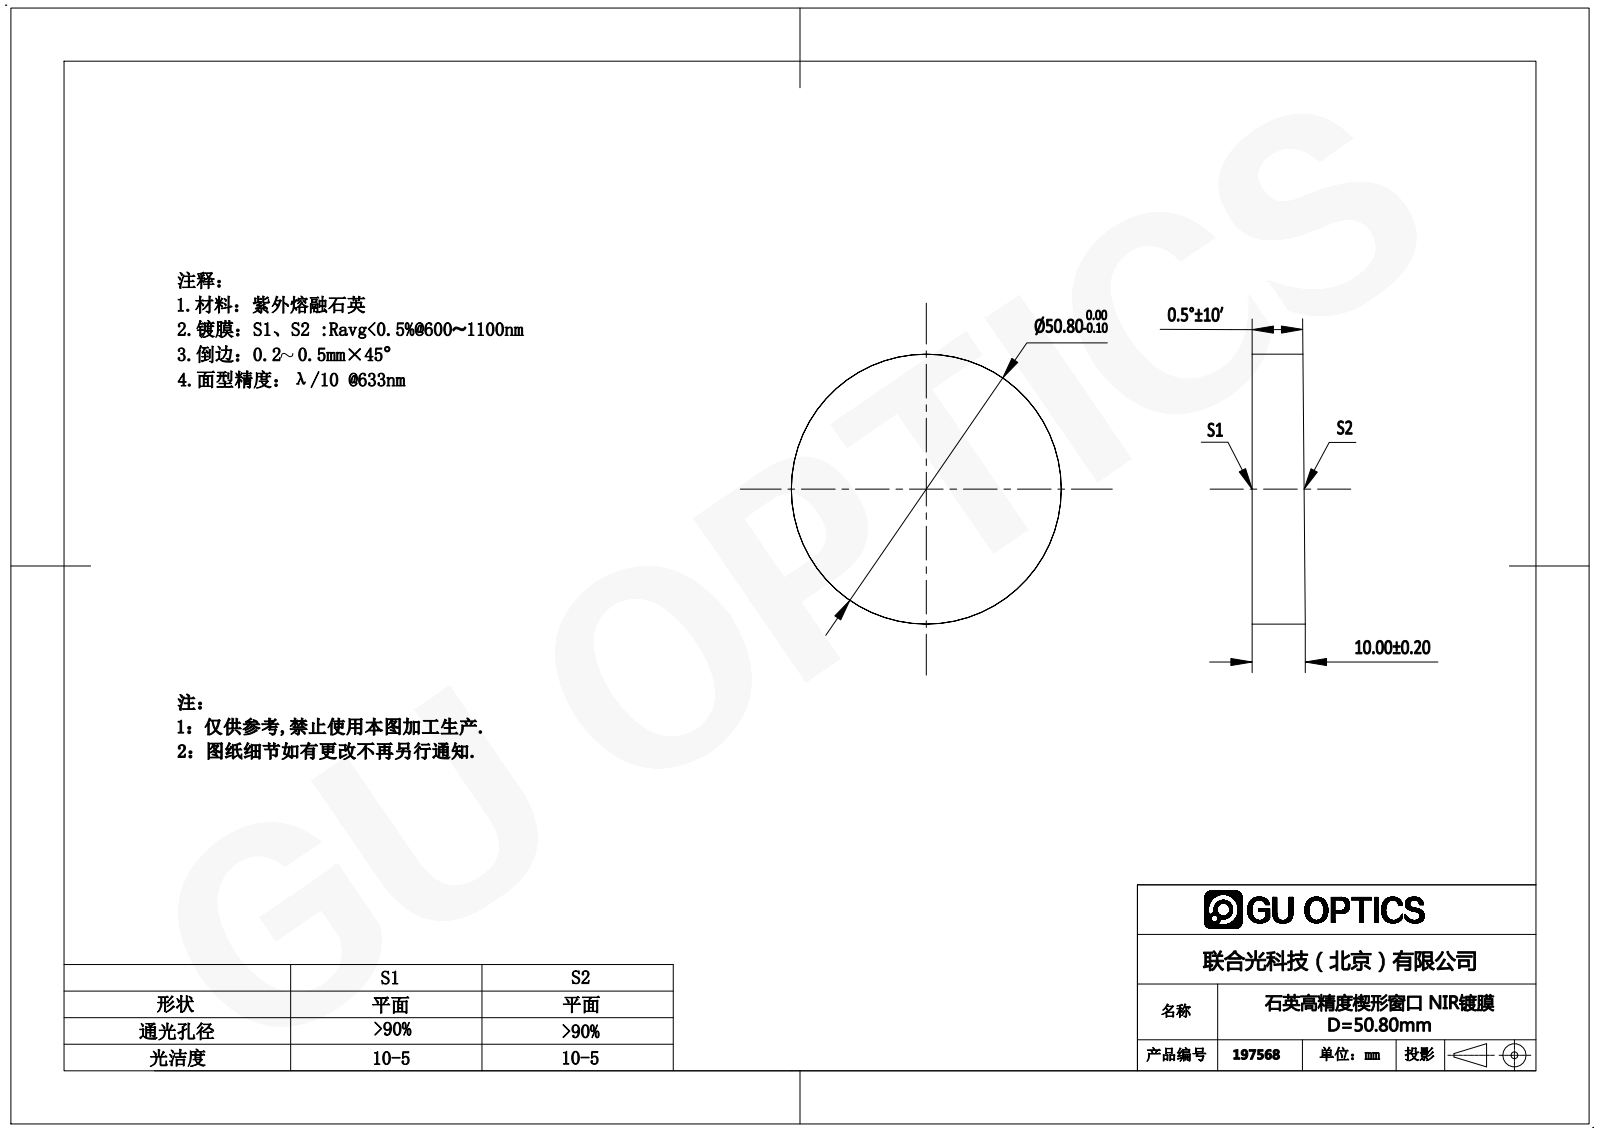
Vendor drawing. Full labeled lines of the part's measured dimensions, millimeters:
Part name (STEP PRODUCT): 197506
STEP written by: SolidWorks 2016 (AUTOMOTIVE_DESIGN)
Units: millimetres
Bodies: 1 solid, 4 faces (2 planar, 2 cylindrical, 0 other)
Overall size (bounding box): 50.8 × 50.8 × 10
Volume: 19 820 mm³ · Surface area: 5 615 mm²
Round bosses / shafts (diameter × count): ⌀50.8 ×1
